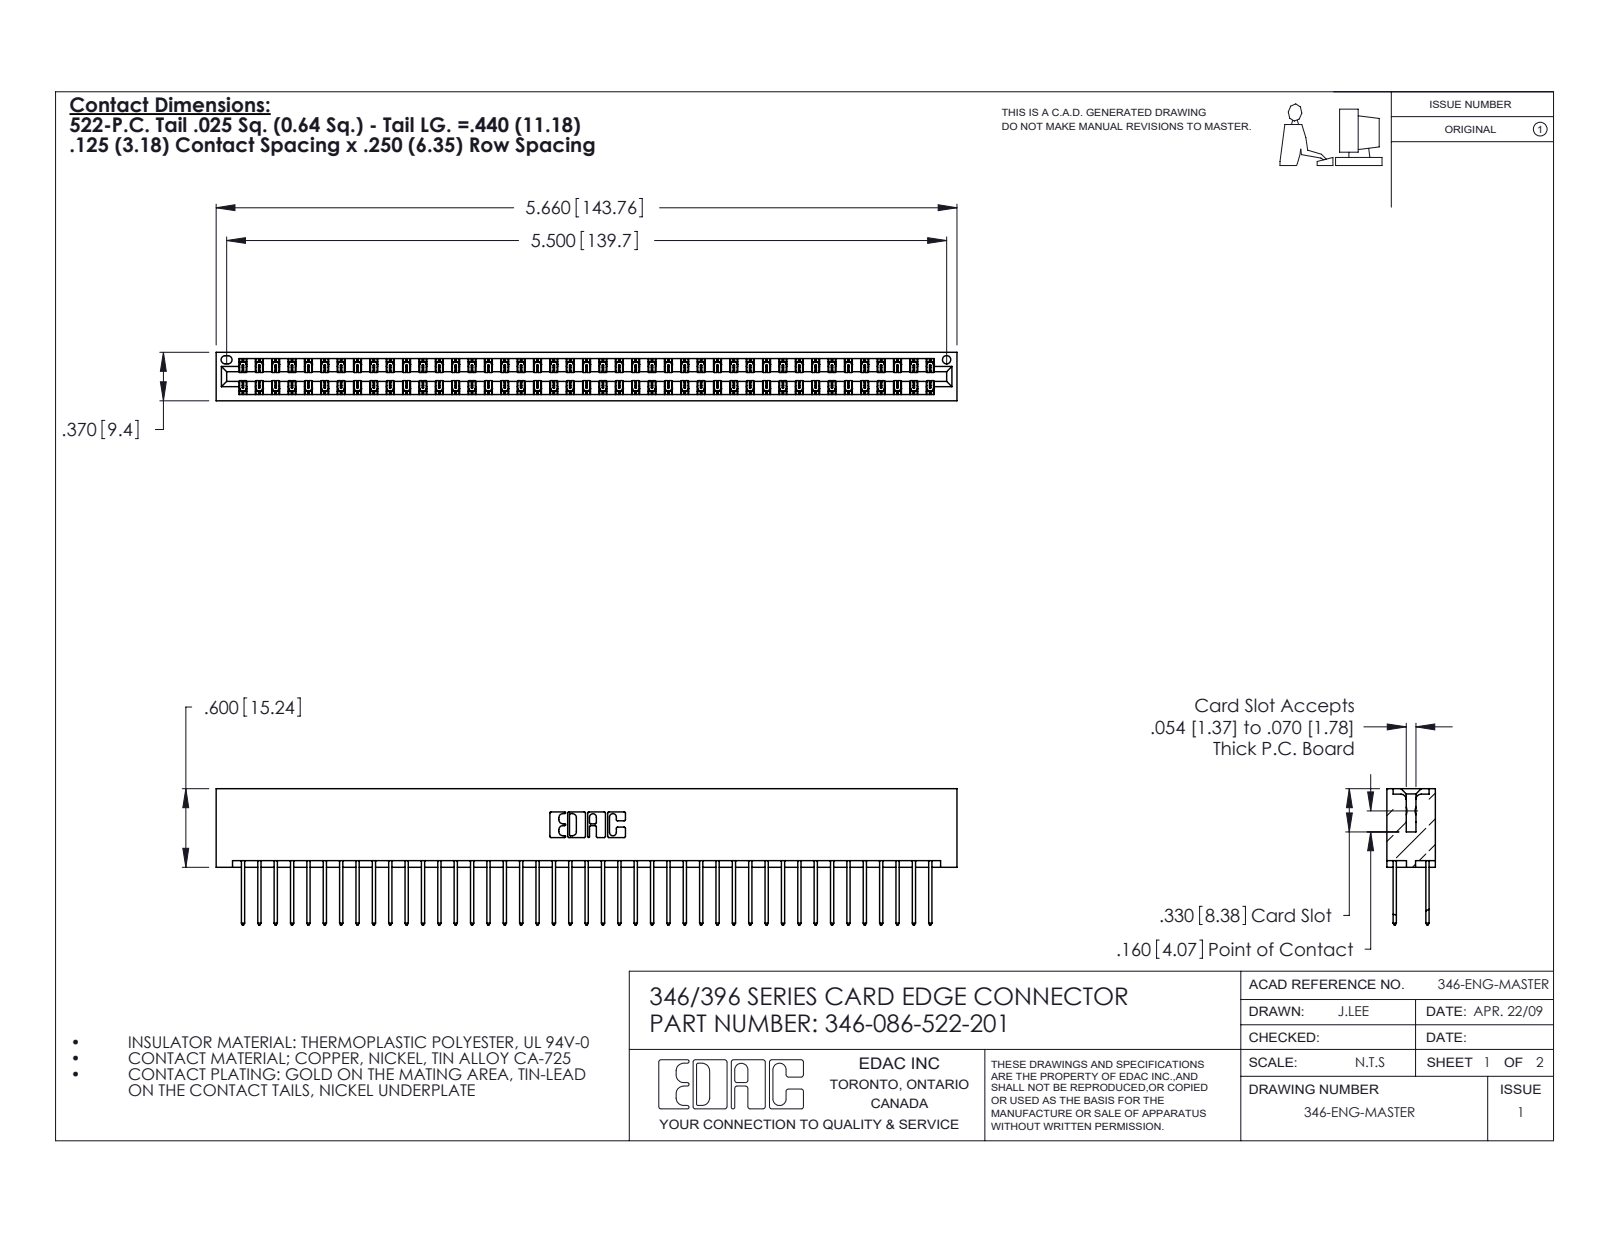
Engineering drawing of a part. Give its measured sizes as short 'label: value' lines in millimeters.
name: 346-086-522-201; 346 Part_No Mounting Lugs; 345-292-001_345-293-122
written by: SolidWorks 2020 (CONFIG_CONTROL_DESIGN)
unit: mm
bodies: 87 solids, 4586 faces (3082 planar, 1504 cylindrical, 0 other)
size: 143.8 × 26.4 × 9.4
volume: 14 800 mm³; area: 21 570 mm²
holes: 1× ⌀1.6
rounds: 129× R0.2, 86× R0.3, 22× R0.3, 6× R0.2, 6× R0.8, 3× R0.7, 2× R0.4, 2× R0.6
face distances: 1.2, 8.2, 6.4, 1.8, 7.6, 0.6, 9.4, 7, 3.8, 5.6
